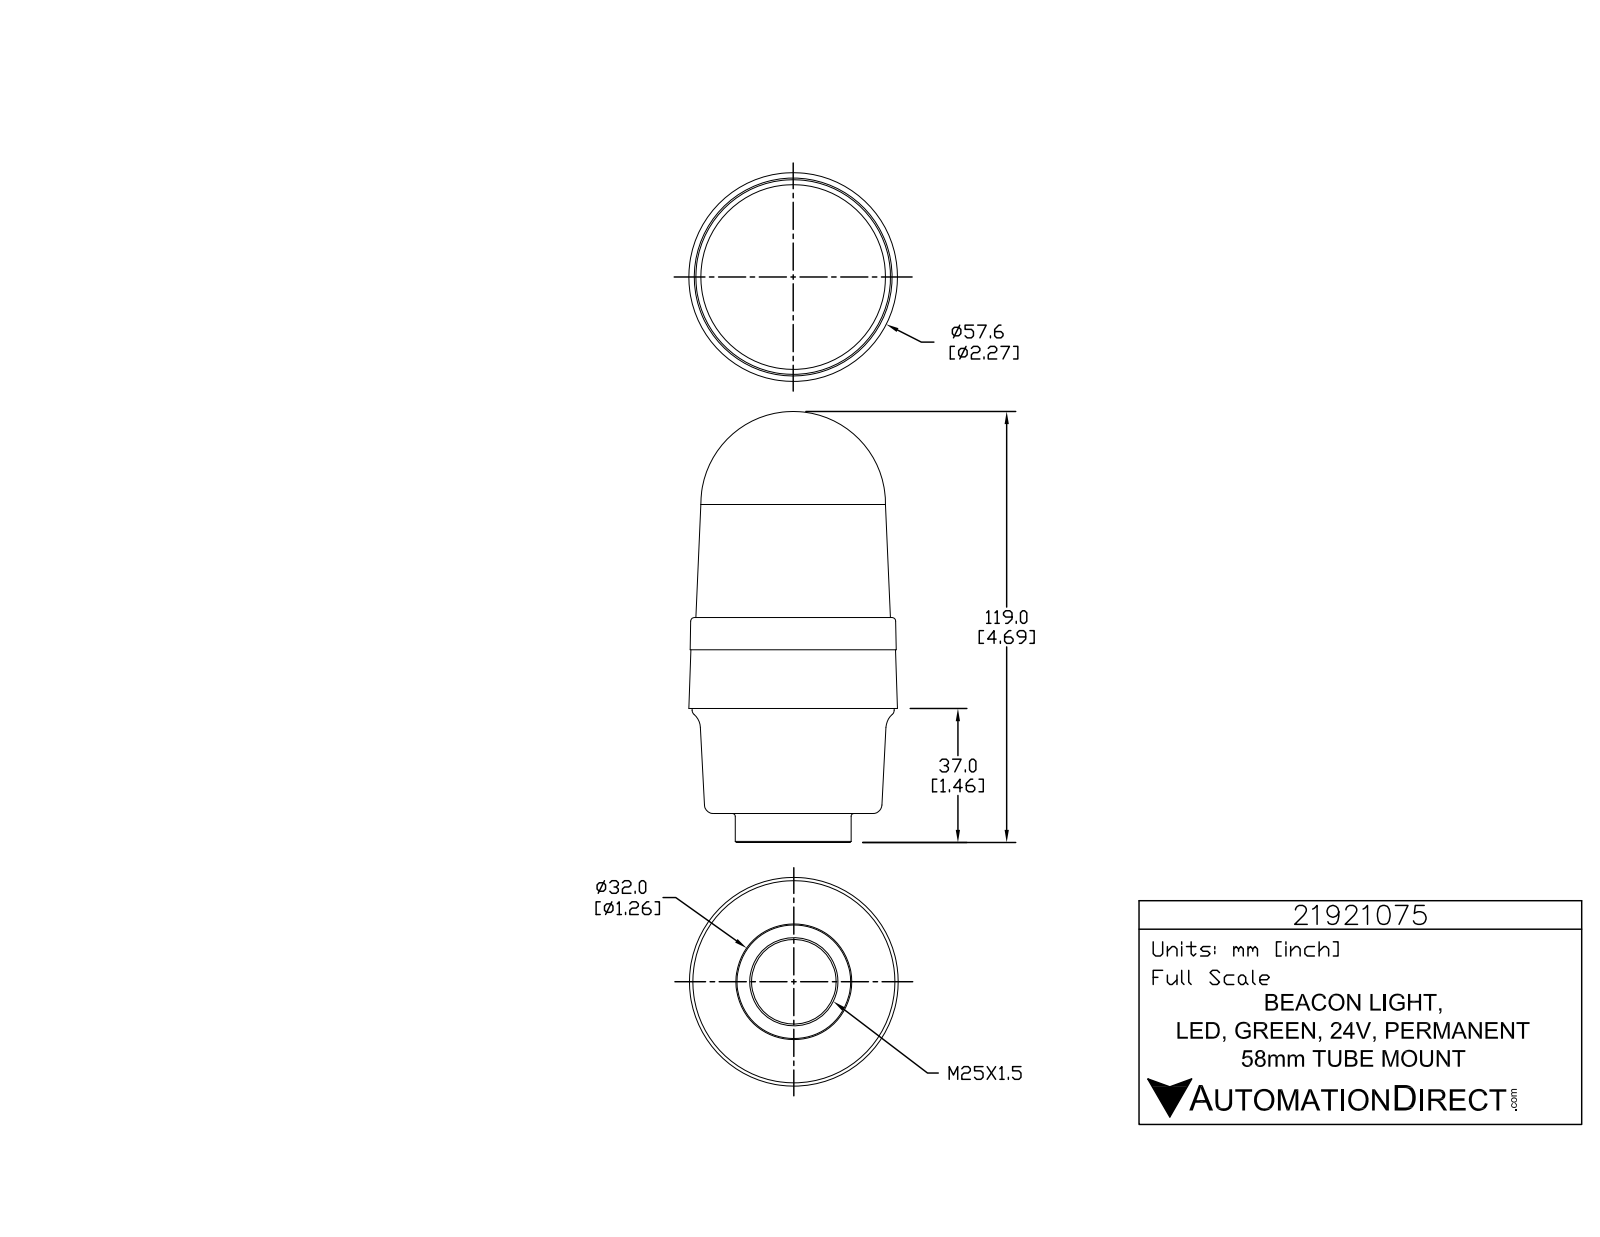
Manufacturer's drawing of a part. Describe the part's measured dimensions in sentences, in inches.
The part is named "21921075". Its 3-D file was written by "SolidWorks 2015 (AUTOMOTIVE_DESIGN)". It is 1 solid with 791 faces: 525 planar, 168 cylindrical and 98 other. Overall it measures 4.685 by 2.269 by 2.269 inches. Its volume is 13.89 cubic inches and its surface area 34.06 square inches. Round holes: 3 of diameter 0.039, 1 of diameter 0.92. Round bosses or shafts: 3 of diameter 0.226, 3 of diameter 0.056, 1 of diameter 2.197, 1 of diameter 1.26. Partial cylindrical surfaces (rounded edges, fillets, slot ends): 6 of radius 0.008, 6 of radius 0.008, 6 of radius 0.008, 6 of radius 0.131, 3 of radius 0.004, 3 of radius 0.005, 3 of radius 0.008, 3 of radius 0.008. The main face-to-face distances are 0.315, 1.142, 1.457, 0.988, 2.13, 2.445, 0.35, 0.638, 1.78, 2.094.
